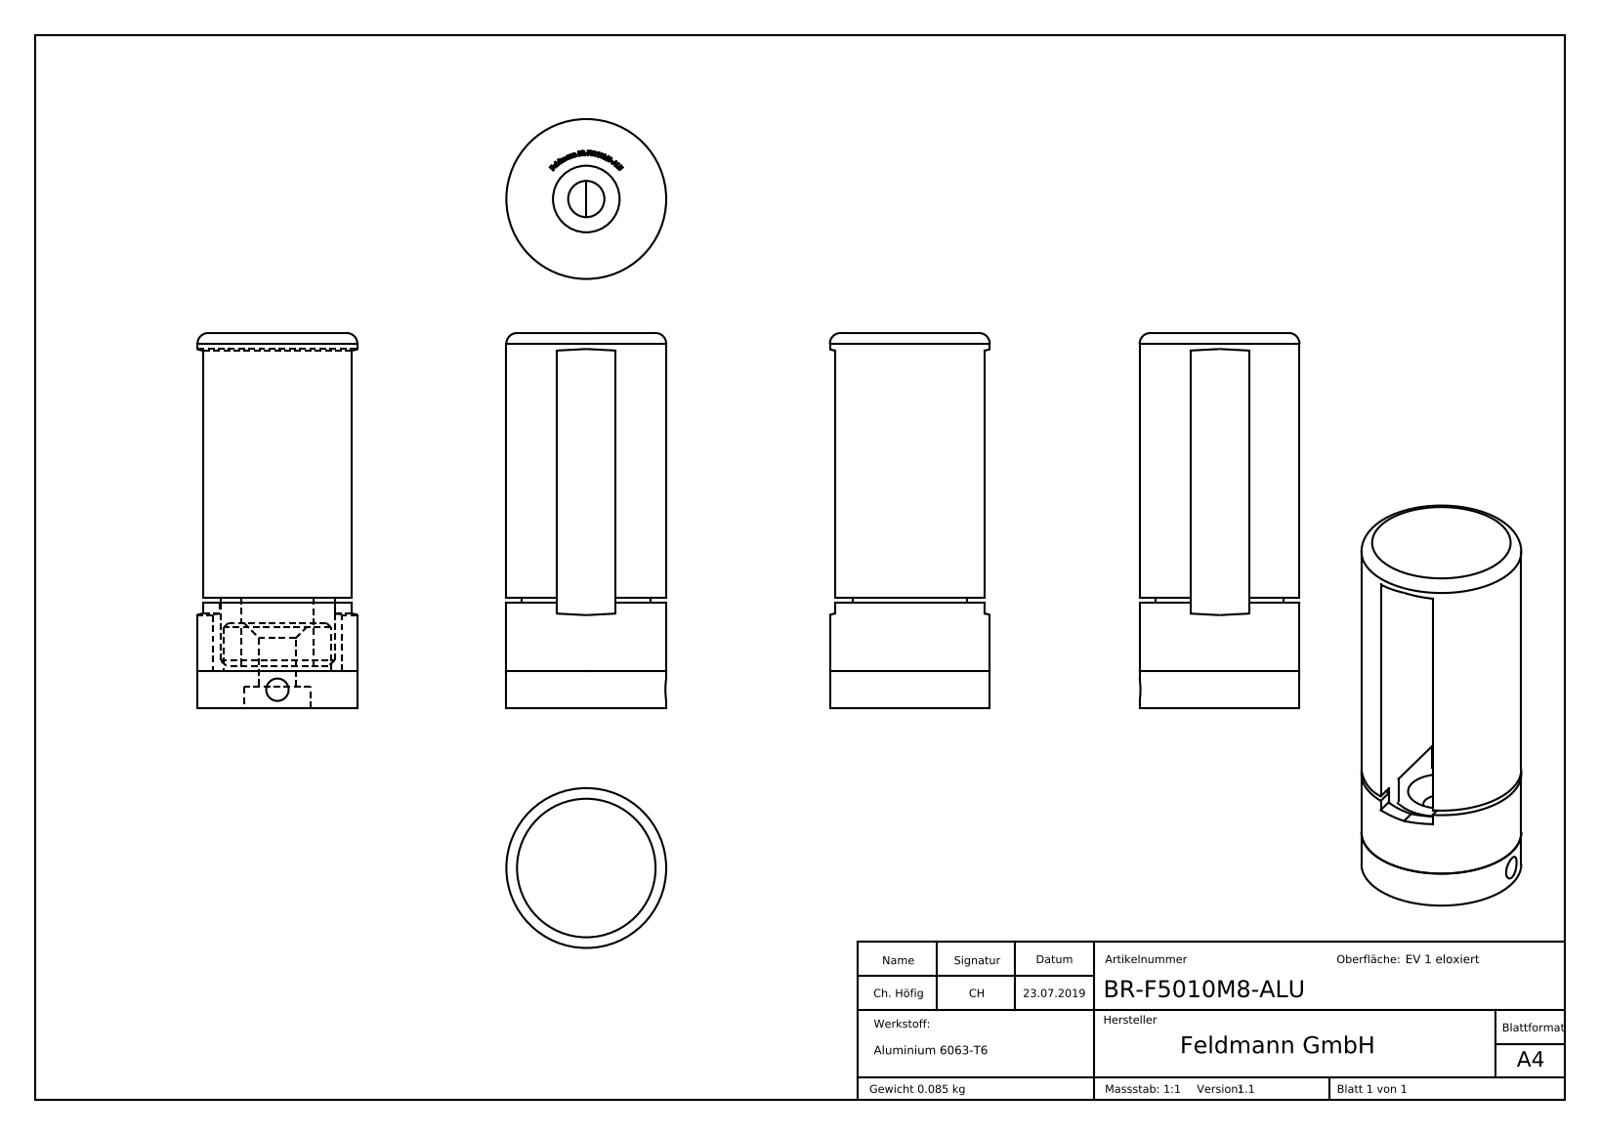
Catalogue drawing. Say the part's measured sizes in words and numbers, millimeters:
The part is named "BR-R1XM8-XXX Teil3; BR-F5010M8-ALU; BR-R1XM8-XXX Teil2; BR-R1XM8-XXX Teil3_BR-F5010M8-ALU Teil3 (+3 more)". Its 3-D file was written by "SolidWorks 2015 (CONFIG_CONTROL_DESIGN)". It is 3 solids with 329 faces: 195 planar, 12 cylindrical and 122 other. Overall it measures 70.45 by 30 by 30 millimeters. Its volume is 31 459 cubic millimeters and its surface area 14 380 square millimeters. Round holes: 1 of diameter 4.2, 1 of diameter 6.8, 1 of diameter 12.5, 1 of diameter 24.2. Round bosses or shafts: 1 of diameter 30, 1 of diameter 20. Partial cylindrical surfaces (rounded edges, fillets, slot ends): 1 of radius 8.75, 1 of radius 12.05. The main face-to-face distances are 11, 7, 70.45, 63.45, 1, 12.8, 20.8, 13.8, 49.65, 19.8.
